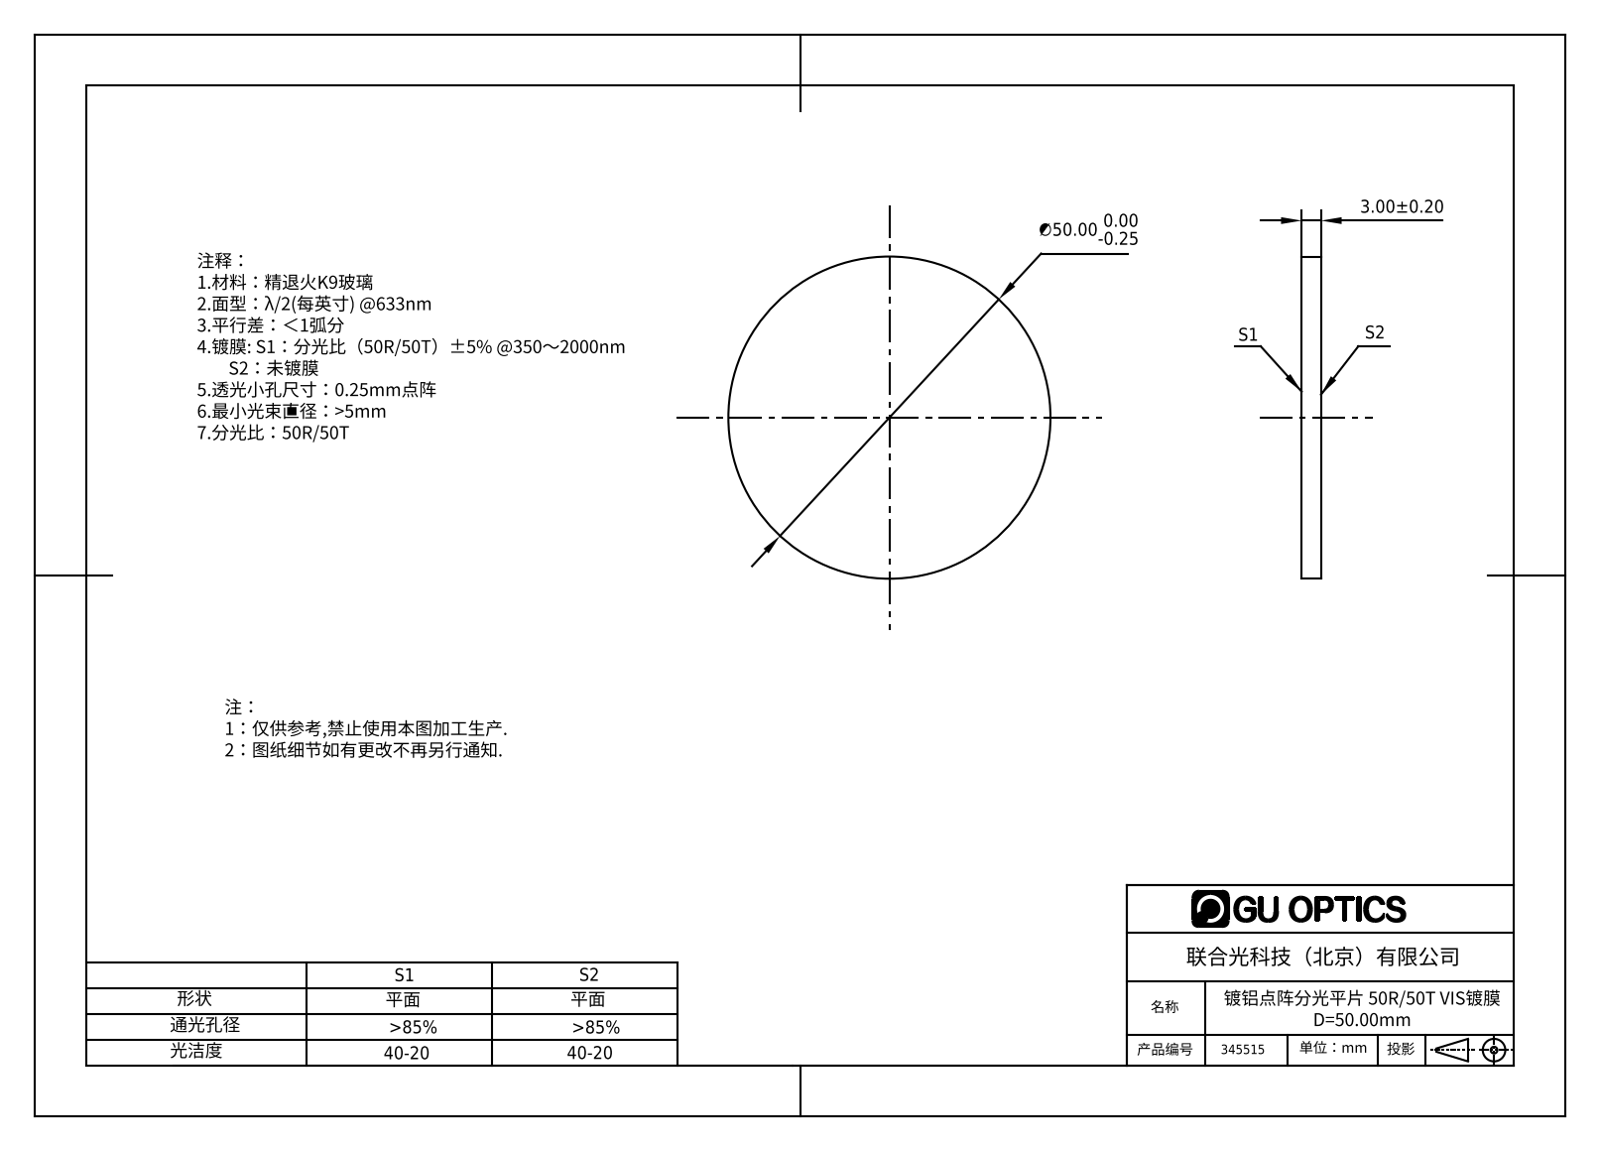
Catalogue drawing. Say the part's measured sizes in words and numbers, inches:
The part is named "345506". Its 3-D file was written by "SolidWorks 2016 (AUTOMOTIVE_DESIGN)". It is 1 solid with 4 faces: 2 planar, 2 cylindrical and 0 other. Overall it measures 1.969 by 1.969 by 0.118 inches. Its volume is 0.359 cubic inches and its surface area 6.817 square inches. Round bosses or shafts: 1 of diameter 1.969. The main face-to-face distances are 0.118.
